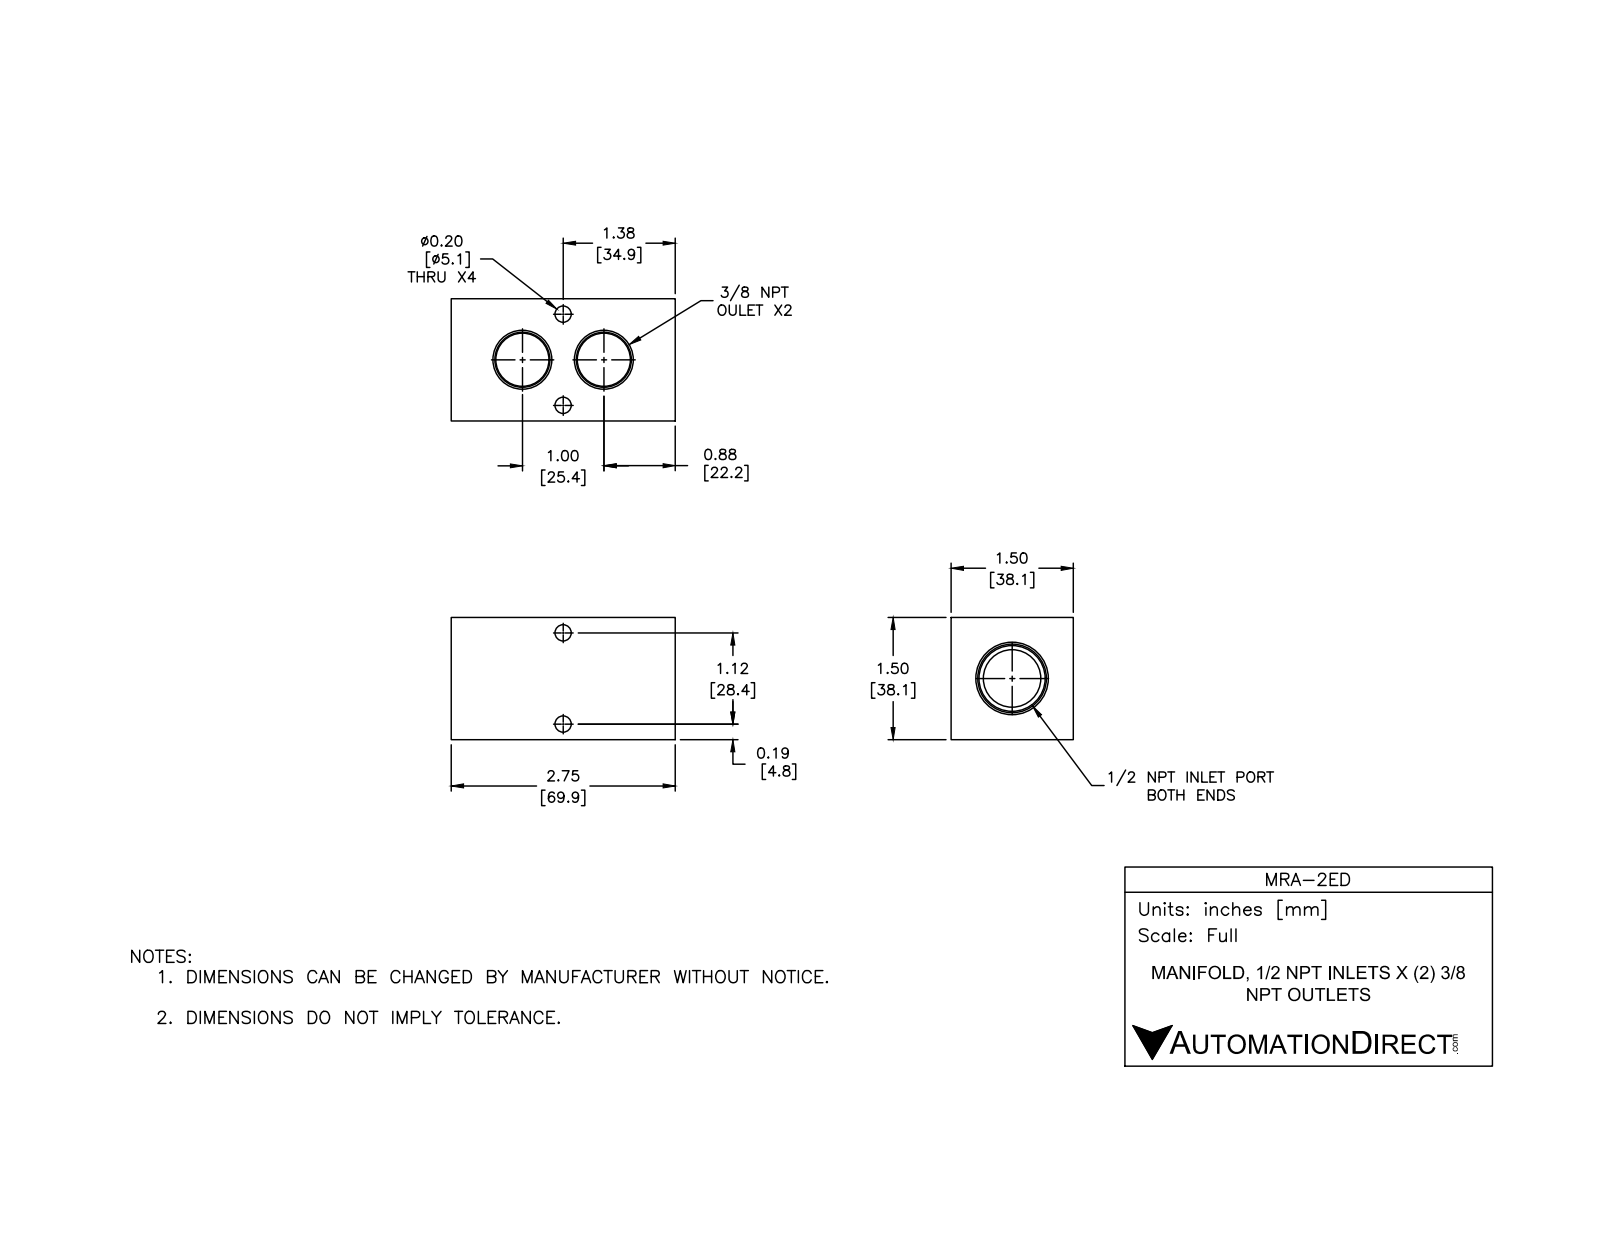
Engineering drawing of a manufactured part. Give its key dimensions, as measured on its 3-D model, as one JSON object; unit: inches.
{"part_name": "MRA-2ED", "step_written_by": "SolidWorks 2015 (CONFIG_CONTROL_DESIGN)", "units": "inches", "bodies": {"solids": 1, "faces": 58, "planar": 12, "cylindrical": 30, "other": 16}, "overall_size": [2.75, 1.5, 1.5], "volume_in3": 4.5, "surface_area_in2": 30.11, "round_holes": [[0.2, 4], [0.562, 2], [0.703, 1]], "face_to_face_distances": [1.5, 2.75, 0.53, 2.22, 1.09, 0.41, 1.69], "hole_center_spacings": [0.751, 1.12, 1]}
